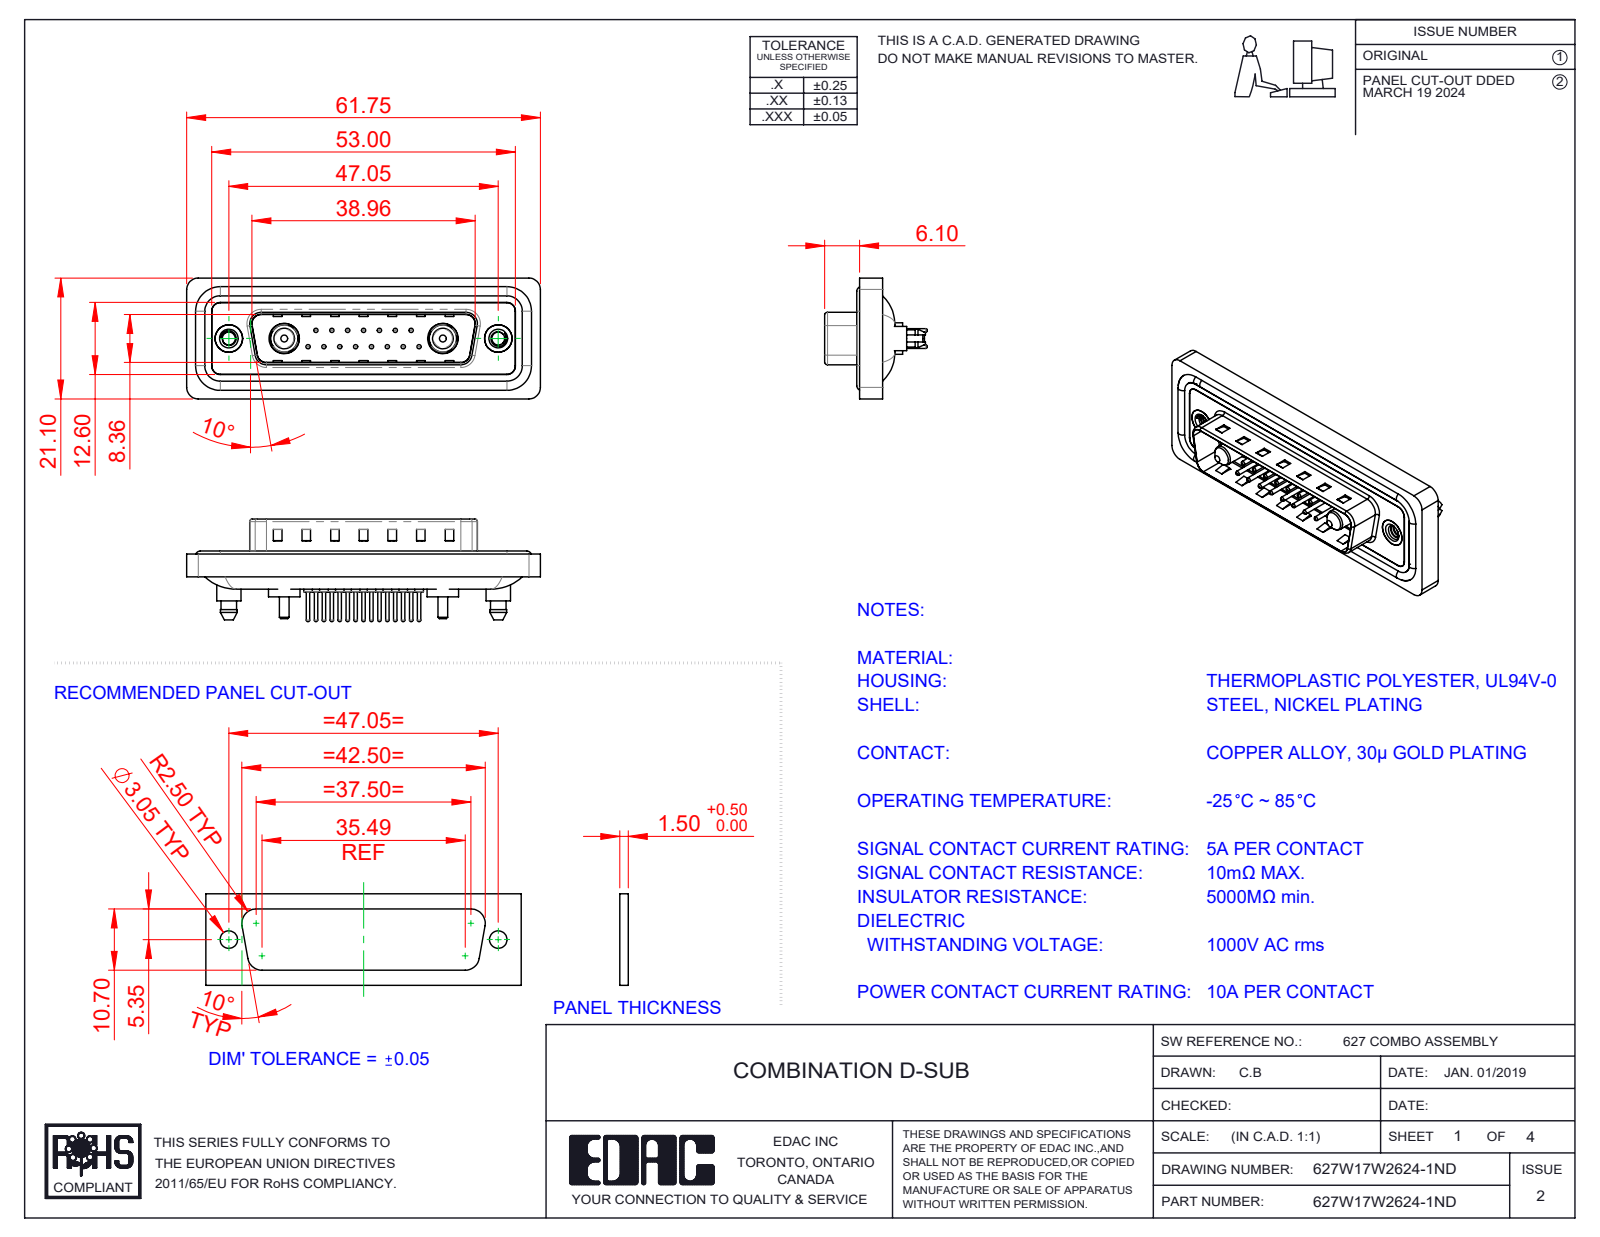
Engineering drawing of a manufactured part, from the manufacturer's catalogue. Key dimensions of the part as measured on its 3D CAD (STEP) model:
Part name (STEP PRODUCT): 627Combo Contact Row 1_24; Power Pin_10A S; 627W17W2624-1ND; 627Combo Contact Row 2_24 (+6 more)
STEP written by: SolidWorks 2023 (CONFIG_CONTROL_DESIGN)
Units: millimetres
Bodies: 26 solids, 1174 faces (350 planar, 476 cylindrical, 348 other)
Overall size (bounding box): 61.75 × 21.1 × 17.9
Volume: 7 372 mm³ · Surface area: 12 225 mm²
Round holes (diameter × count): ⌀0.75 ×15, ⌀1.6 ×15, ⌀2 ×15, ⌀2.26 ×2, ⌀4 ×2, ⌀4.8 ×2, ⌀4.85 ×2, ⌀5 ×2, ⌀5.3 ×2
Round bosses / shafts (diameter × count): ⌀1.5 ×15, ⌀0.6 ×15, ⌀1.6 ×4, ⌀5.5 ×2, ⌀5.4 ×2, ⌀5.2 ×2, ⌀4.9 ×2, ⌀4.75 ×2
Partial cylindrical surfaces — rounded edges, fillets, slot ends (radius × count): R1.5 ×24, R2 ×18, R1.6 ×10, R0.5 ×8, R0.25 ×4, R0.6 ×4, R0.65 ×4, R0.9 ×4
Main face-to-face distances: 0.4, 1.5, 1.1, 1.6, 0.5, 3.1, 2.9, 0.82, 9.58, 4.1
Hole centre spacings: 3.16, 2.77, 5.54, 8.31, 5.04, 7.49, 11.08, 5.03
